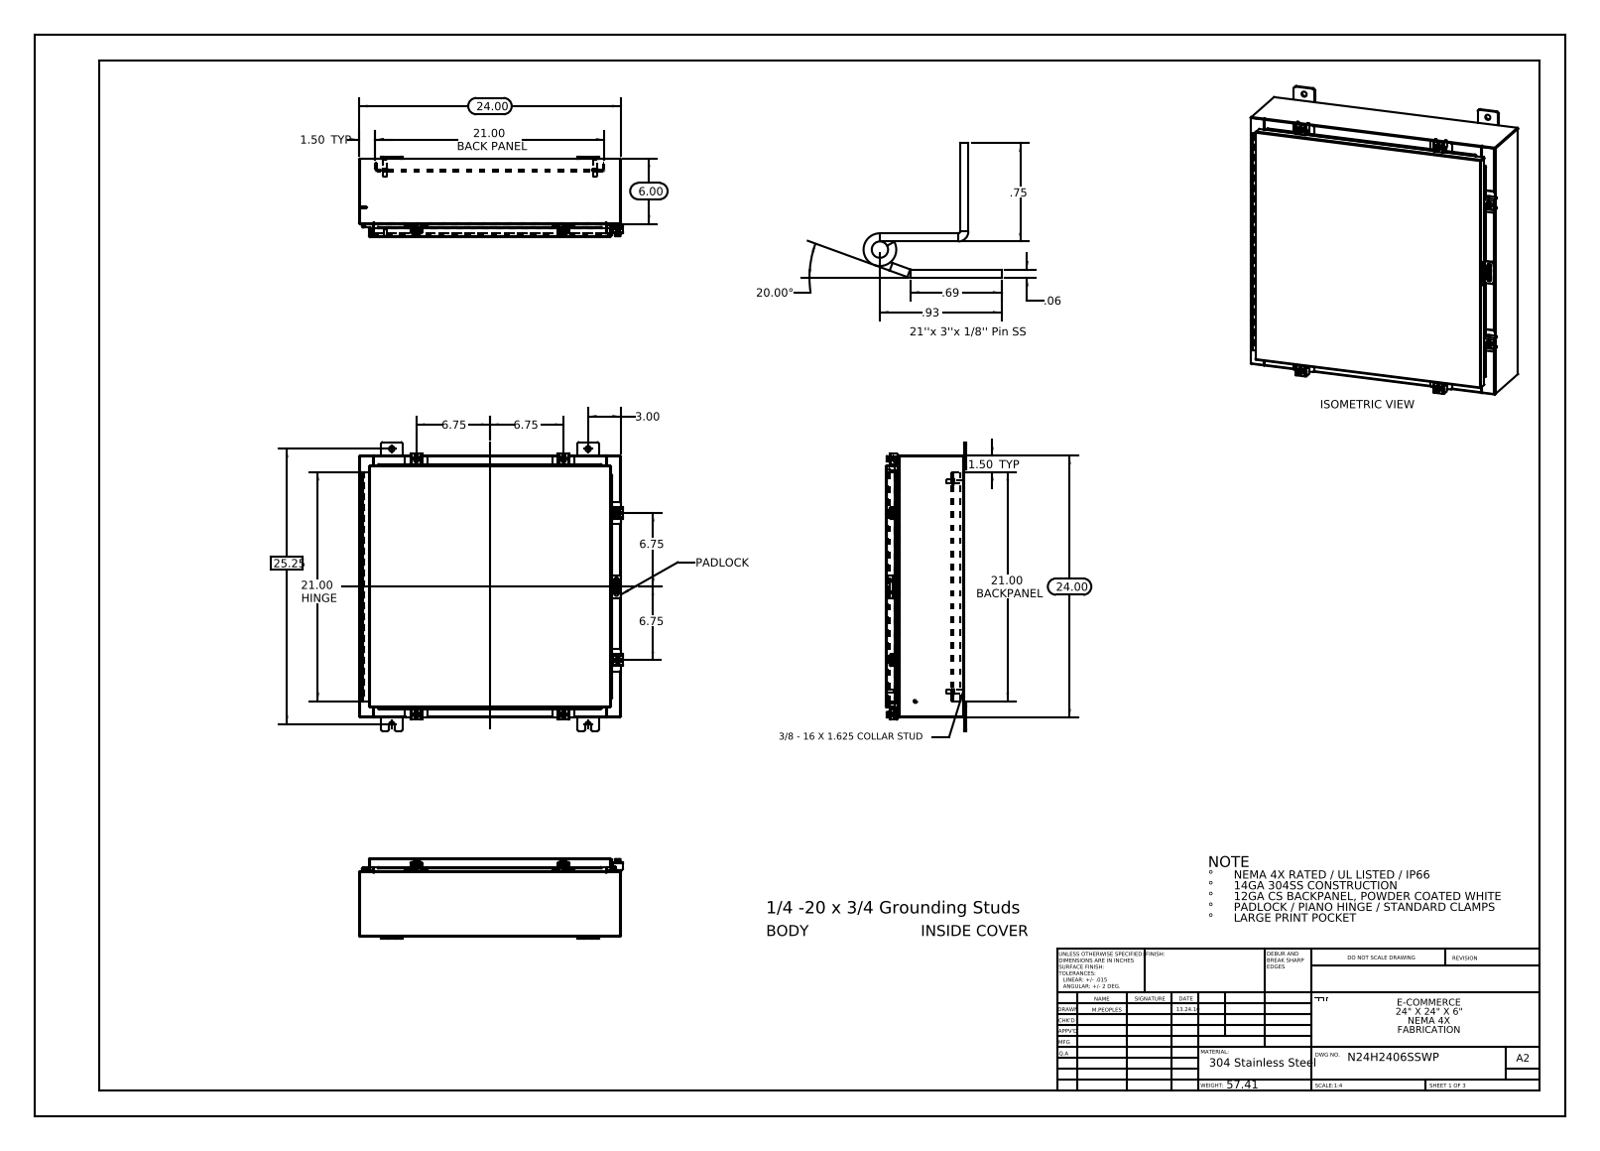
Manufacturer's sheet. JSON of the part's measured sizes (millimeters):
{"part_name": "N24H2406SSWP Top; N24H2406SSWP Standard Clamps; N24H2406SSWP Mounting Feet; N24H2406SSWP Bottom (+8 more)", "step_written_by": "SolidWorks 2013 (CONFIG_CONTROL_DESIGN)", "units": "millimeters", "bodies": {"solids": 49, "faces": 1735, "planar": 914, "cylindrical": 713, "other": 108}, "overall_size": [673.1, 615, 187.7], "volume_mm3": 3310000, "surface_area_mm2": 3257000, "round_holes": [[12.7, 8], [5.4, 6], [6.6, 6], [3.2, 2]], "round_bosses_or_shafts": [[6.4, 7], [12.7, 6], [10.1, 6], [15.9, 4], [9.5, 4], [8.4, 4], [8, 2], [6, 2]], "partial_cylinders_radius": [[1.5, 30], [0.3, 25], [4.8, 24], [2.2, 21], [3, 12], [3.6, 12], [3.2, 10], [1.3, 9]], "face_to_face_distances": [1.9, 181, 607.7, 179.1, 182.9, 2.6, 25.4, 27.3, 153.7, 155.6], "hole_center_spacings": [419.3, 486, 547.2, 683.4, 342.9, 47.2, 57.8, 61.5]}
